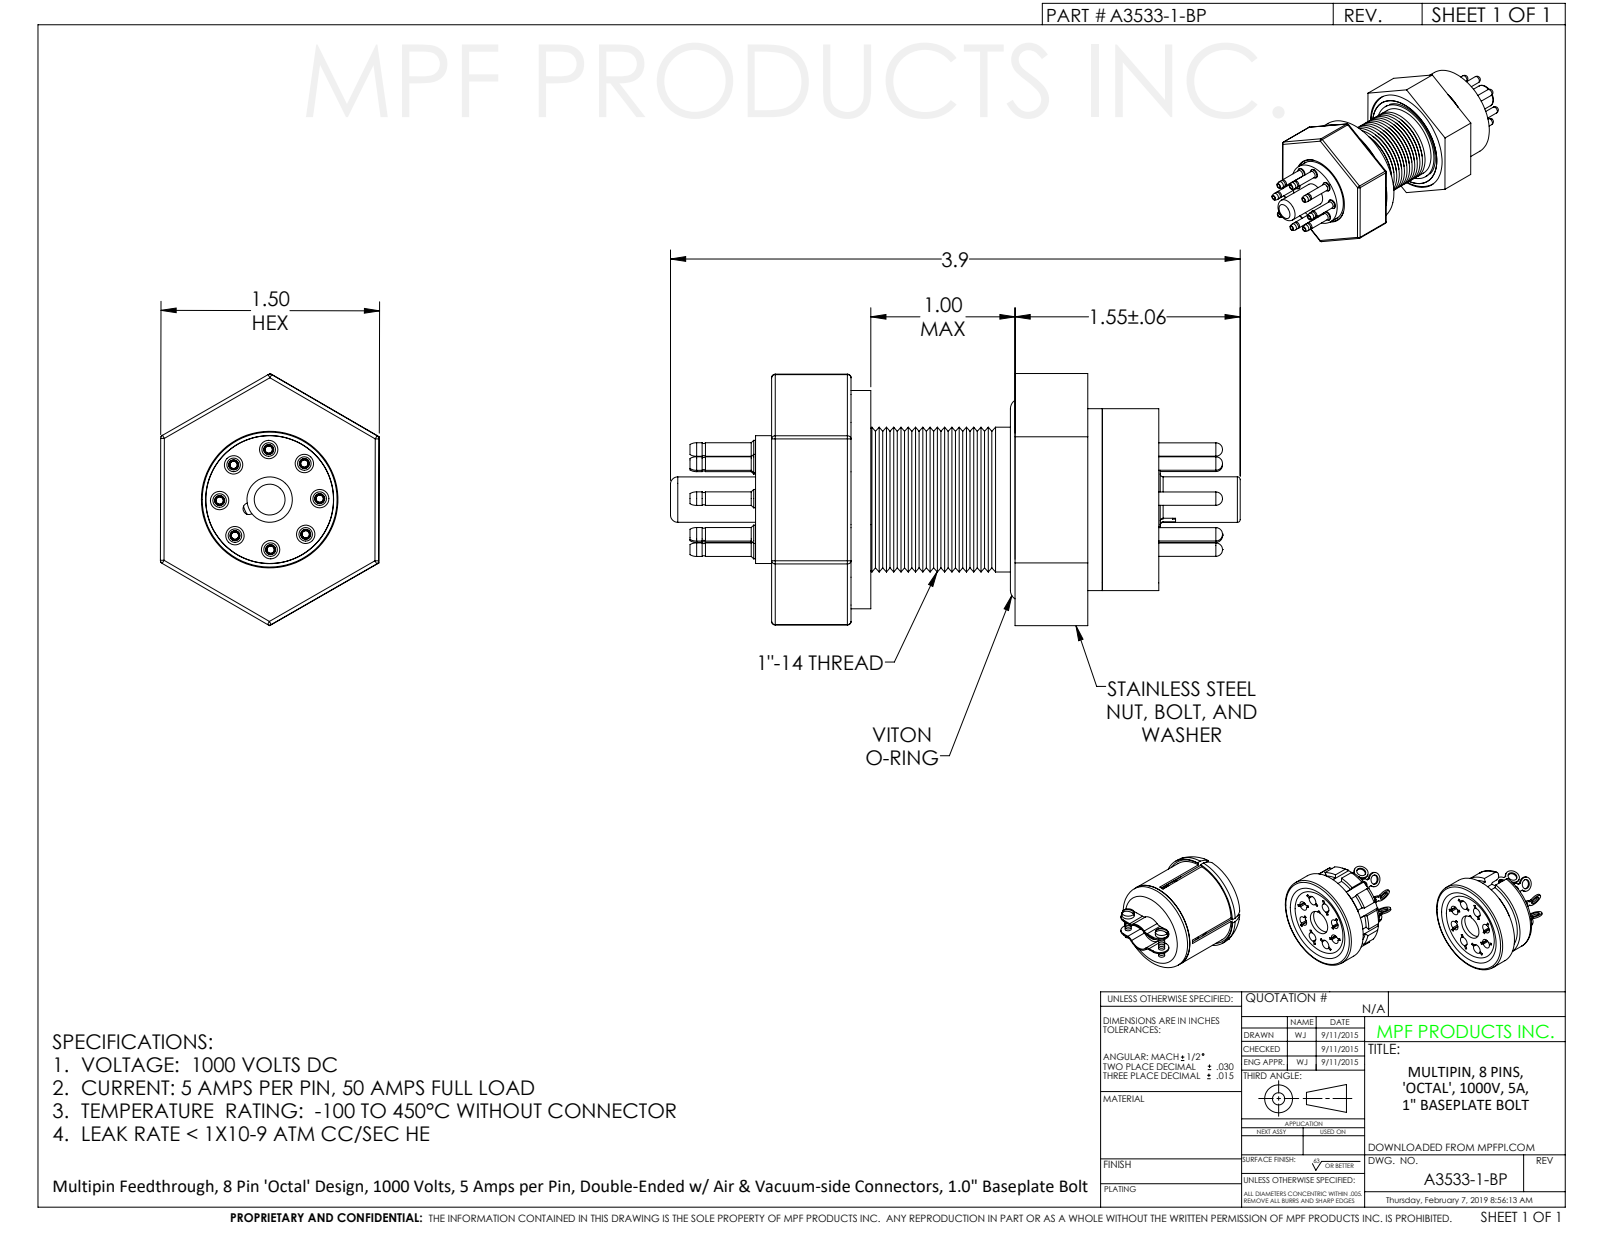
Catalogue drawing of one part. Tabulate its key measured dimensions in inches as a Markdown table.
| quantity | value |
| --- | --- |
| part name | A3533-1-BP |
| STEP written by | SolidWorks 2012 (CONFIG_CONTROL_DESIGN) |
| units | inches |
| bodies | 1 solid, 624 faces (116 planar, 218 cylindrical, 290 other) |
| overall size | 3.917 × 1.732 × 1.504 |
| volume | 3.637 in³ |
| surface area | 31.86 in² |
| round holes (diameter × count) | 0.09 × 8, 0.15 × 8, 0.162 × 1, 0.254 × 1, 0.273 × 1, 0.285 × 1, 1.004 × 1, 1.185 × 1, 1.39 × 1 |
| round bosses / shafts (diameter × count) | 0.187 × 8, 0.126 × 8, 0.093 × 8, 0.092 × 8, 0.086 × 8, 1.5 × 1, 1.369 × 1, 1.25 × 1 |
| partial cylindrical surfaces (radius × count) | 0.025 × 18, 0.03 × 4, 0.009 × 2, 0.05 × 2, 0.04 × 1 |
| main face-to-face distances | 1.5, 0.682, 2.542, 1.86, 1.5, 2.174, 1.492, 0.368, 1.781, 1.099 |
| hole center spacings | 0.26, 0.628, 0.34, 0.481, 0.481, 0.34, 0.68, 0.68 |
